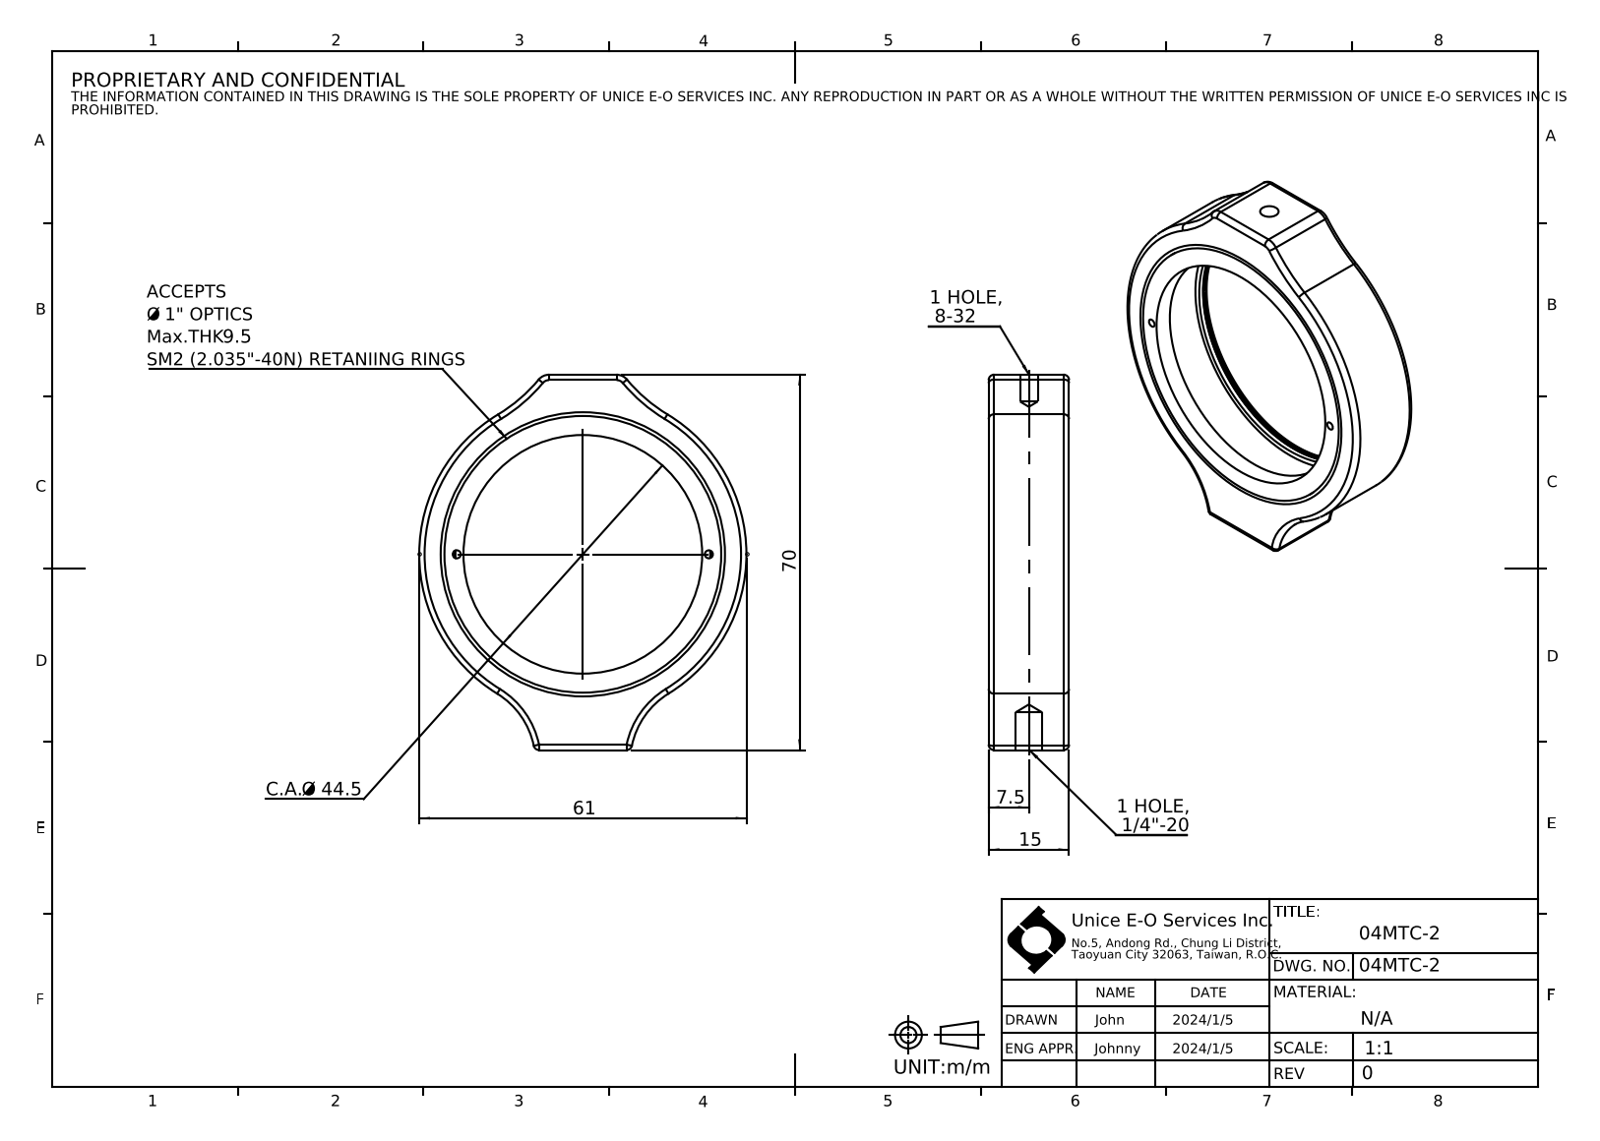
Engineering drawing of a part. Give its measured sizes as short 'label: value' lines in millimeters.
name: 04MTC-2
written by: SolidWorks 2016 (CONFIG_CONTROL_DESIGN)
unit: mm
bodies: 3 solids, 78 faces (9 planar, 35 cylindrical, 34 other)
size: 70 × 61 × 15
volume: 18 259 mm³; area: 10 824 mm²
holes: 2× ⌀1.5, 1× ⌀3.45, 1× ⌀5.11, 1× ⌀44.5, 1× ⌀47.5, 1× ⌀48, 1× ⌀51
bosses: 1× ⌀51.6, 1× ⌀50
rounds: 6× R1, 2× R2.5, 2× R15, 2× R30, 1× R30.5
face distances: 15, 1, 11.5, 3.5, 10.5, 14, 70, 2, 9.5, 13
hole spacings: 23.5, 47
